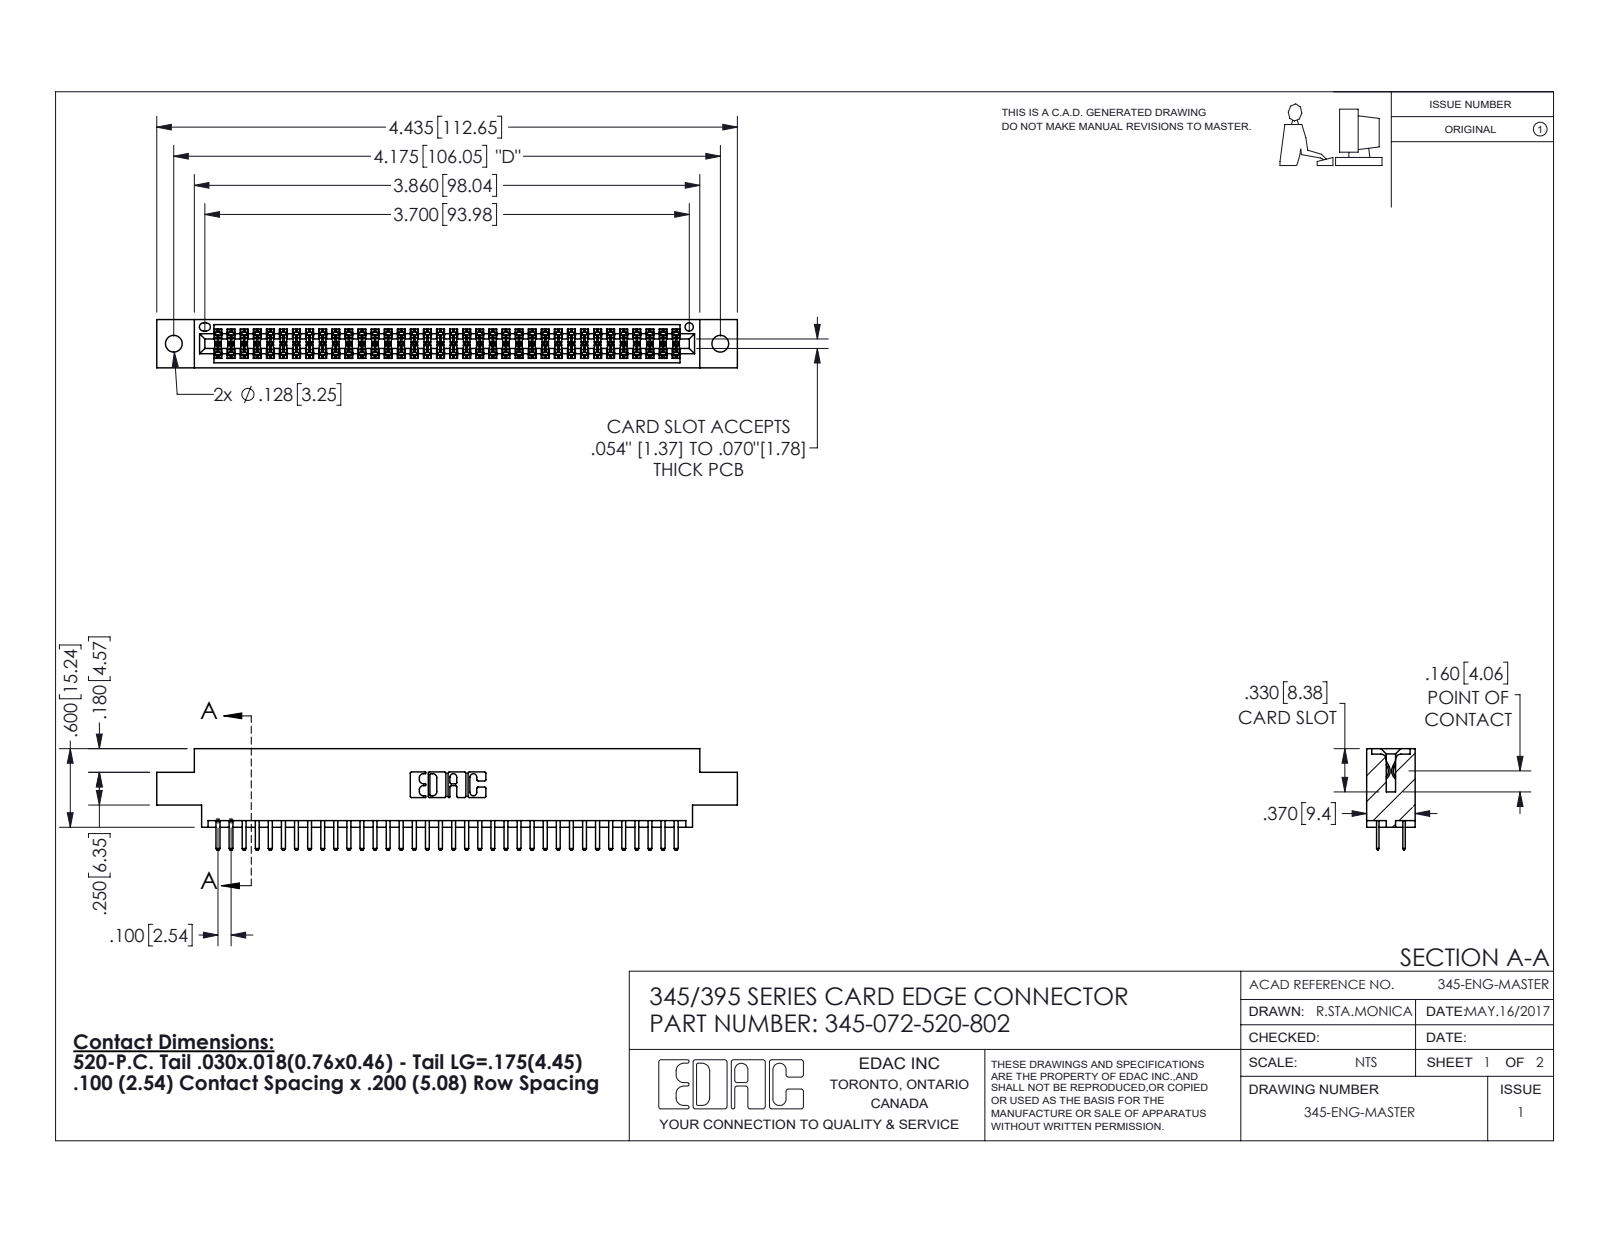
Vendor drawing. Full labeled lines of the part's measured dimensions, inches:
Part name (STEP PRODUCT): 345-292-001_345-293-120; 345-072-520-802; 345 Part_0.170 Offset - 0.128 Dia
STEP written by: SolidWorks 2016 (CONFIG_CONTROL_DESIGN)
Units: inches
Bodies: 73 solids, 4018 faces (2604 planar, 1414 cylindrical, 0 other)
Overall size (bounding box): 4.435 × 0.775 × 0.37
Volume: 0.653 in³ · Surface area: 24.04 in²
Round holes (diameter × count): ⌀0.128 ×2, ⌀0.064 ×1
Partial cylindrical surfaces — rounded edges, fillets, slot ends (radius × count): R0.006 ×108, R0.01 ×76, R0.01 ×22, R0.007 ×6, R0.031 ×6, R0.026 ×3, R0.014 ×2, R0.019 ×2
Main face-to-face distances: 0.072, 0.298, 0.2, 0.37, 0.098, 0.272, 0.025, 0.225, 0.022, 0.175
Hole centre spacings: 0.27, 3.939, 4.175
